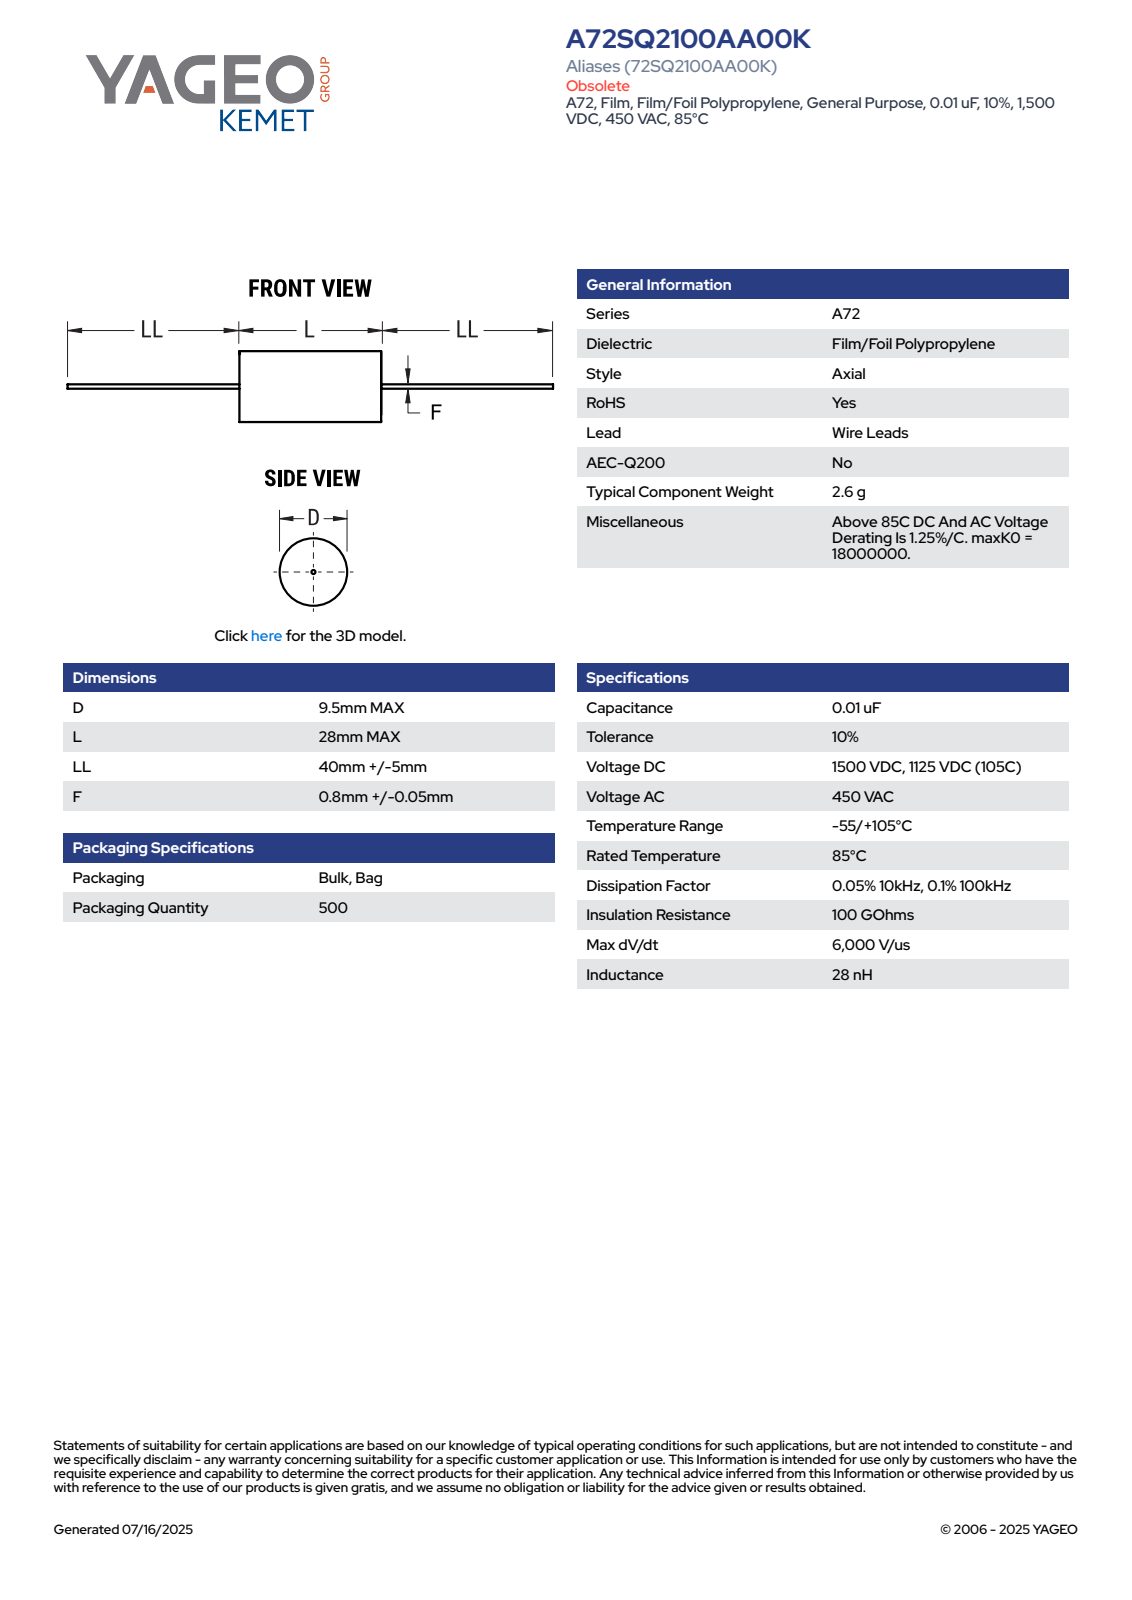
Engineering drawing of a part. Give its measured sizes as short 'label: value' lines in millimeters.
name: CFA_ACWF_9.5X28_D9.5L28LL45F0.85
written by: SolidWorks 2014 (AUTOMOTIVE_DESIGN)
unit: mm
bodies: 1 solid, 72 faces (26 planar, 15 cylindrical, 31 other)
size: 118 × 9.51 × 9.5
volume: 2 036 mm³; area: 1 218 mm²
bosses: 1× ⌀9.5, 1× ⌀0.85
rounds: 1× R4.76
face distances: 28, 45, 73, 118
